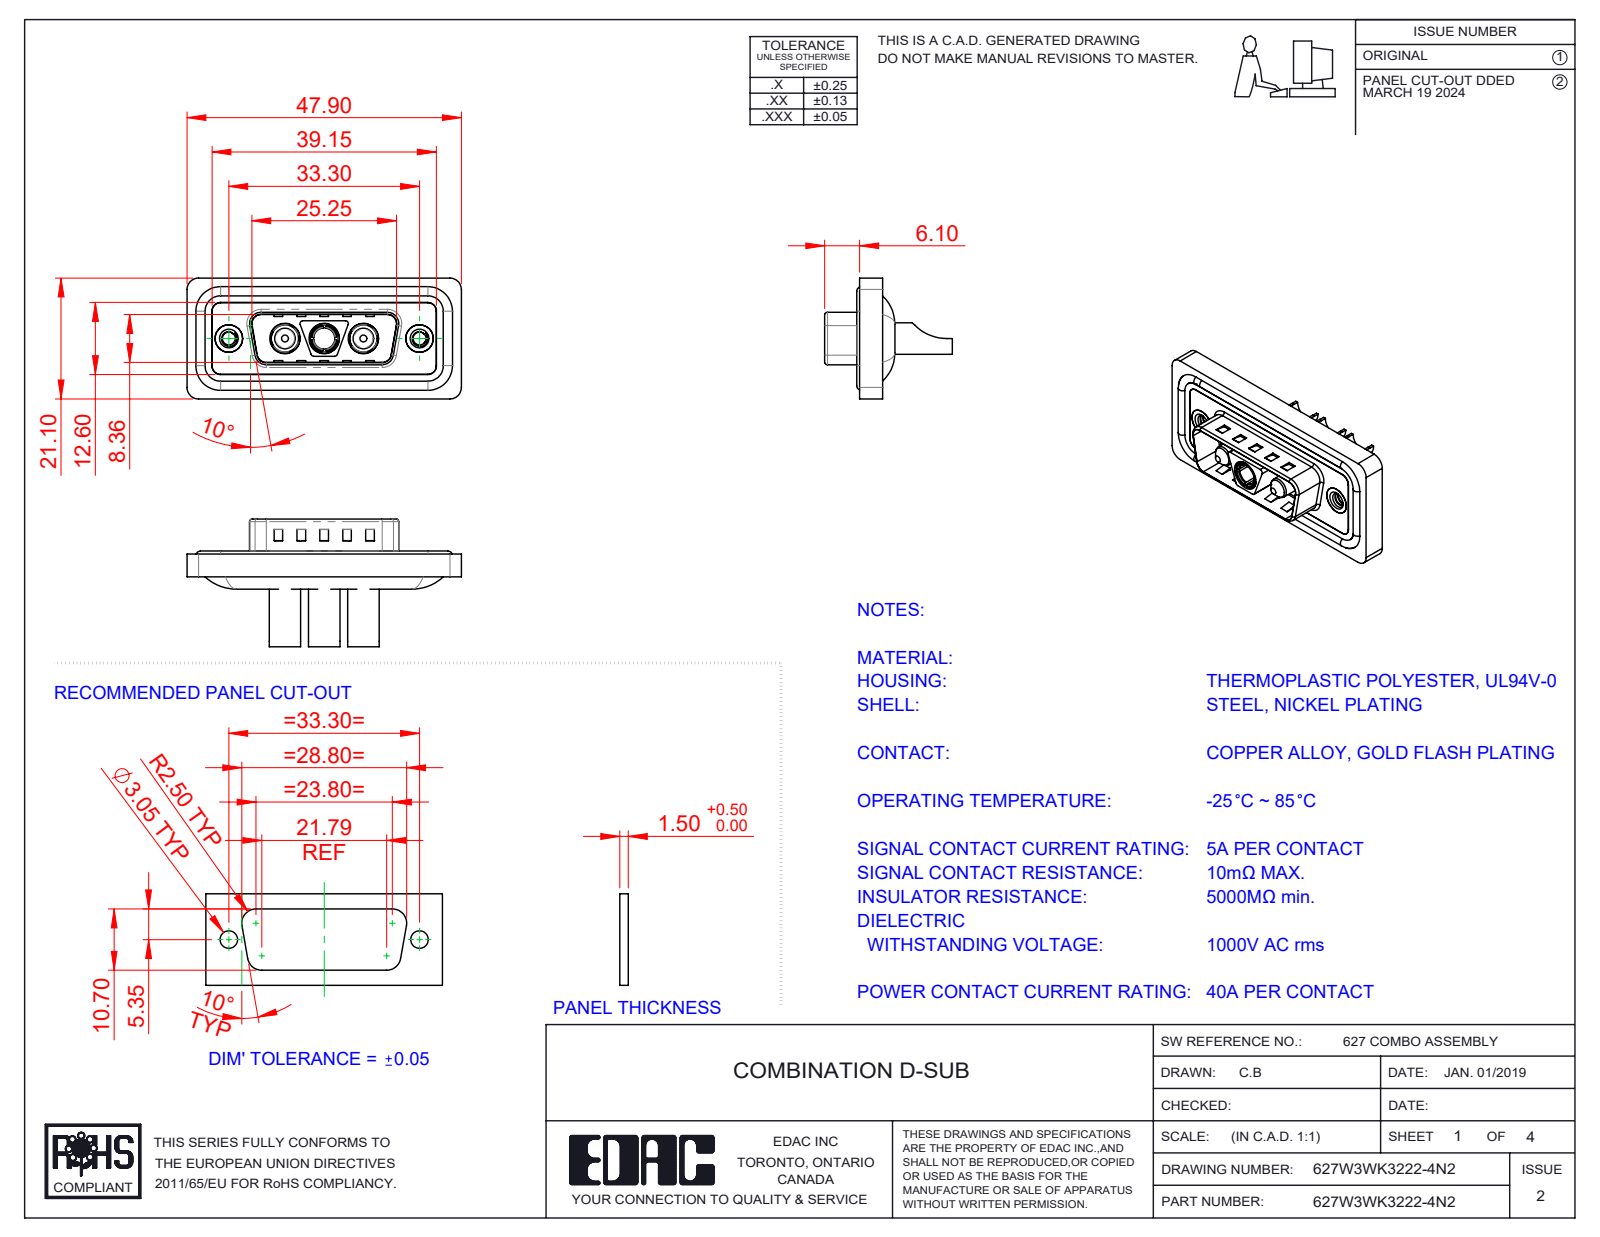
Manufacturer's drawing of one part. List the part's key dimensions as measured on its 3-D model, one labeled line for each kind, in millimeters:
Part name (STEP PRODUCT): Power Pin_40A SC; 627Combo Shell Rear_15 Contacts; 627Combo Waterproof Housing_15 Contacts; 627W3WK3222-4N2 (+4 more)
STEP written by: SolidWorks 2023 (CONFIG_CONTROL_DESIGN)
Units: millimetres
Bodies: 13 solids, 621 faces (237 planar, 253 cylindrical, 131 other)
Overall size (bounding box): 47.9 × 22.3 × 21.1
Volume: 5 808 mm³ · Surface area: 9 547 mm²
Round holes (diameter × count): ⌀4.6 ×3, ⌀4.85 ×3, ⌀5.3 ×3, ⌀2.26 ×2, ⌀4 ×2, ⌀4.8 ×2, ⌀5 ×2, ⌀3.7 ×1
Round bosses / shafts (diameter × count): ⌀1.6 ×4, ⌀5.5 ×3, ⌀5.2 ×3, ⌀4.75 ×3, ⌀3.75 ×3, ⌀4.9 ×2, ⌀3.6 ×2, ⌀4.96 ×1
Partial cylindrical surfaces — rounded edges, fillets, slot ends (radius × count): R1.5 ×26, R2 ×20, R0.5 ×12, R1.6 ×8, R0.25 ×4, R0.6 ×4, R0.65 ×4, R0.9 ×4
Main face-to-face distances: 0.4, 1.1, 0.5, 1.6, 3.1, 2.9, 1.5, 0.82, 9.58, 2.5
Hole centre spacings: 6.85, 9.8, 16.65, 23.5, 13.7, 33.3
